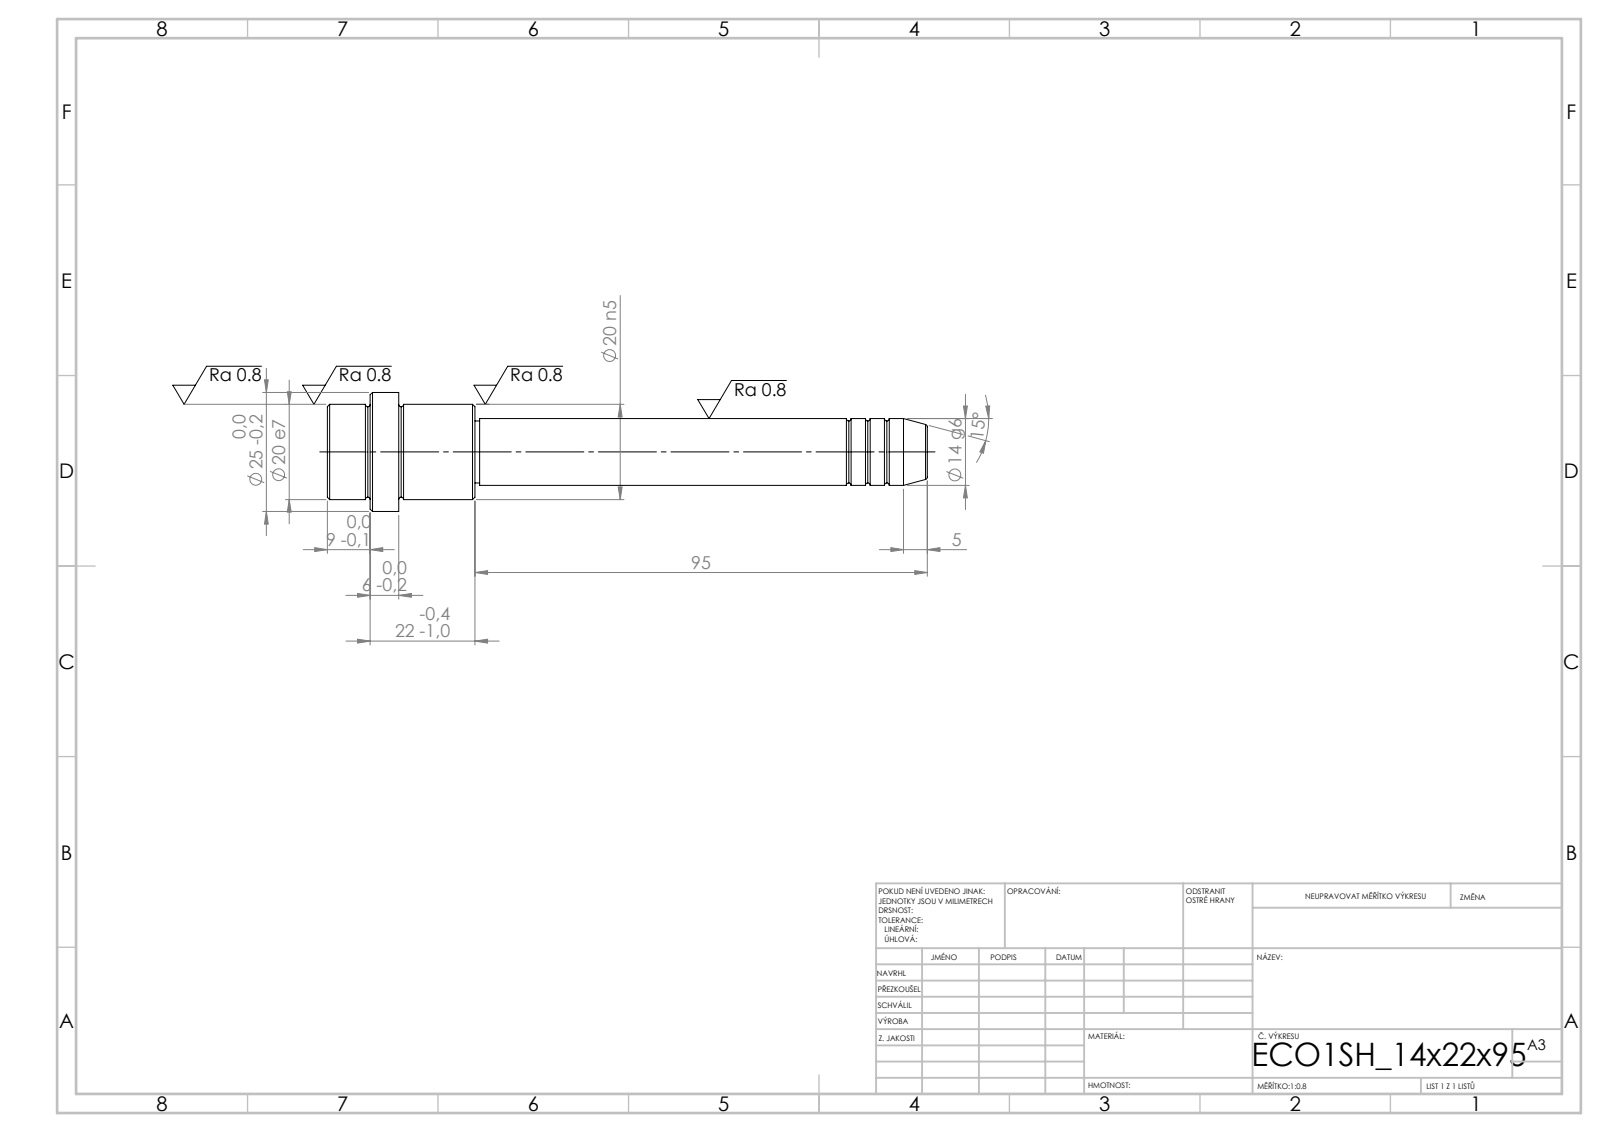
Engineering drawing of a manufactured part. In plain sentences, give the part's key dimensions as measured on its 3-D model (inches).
Its 3-D file was written by "SolidWorks 2019 (CONFIG_CONTROL_DESIGN)". It is 1 solid with 52 faces: 6 planar, 16 cylindrical and 30 other. Overall it measures 4.961 by 0.984 by 0.984 inches. Its volume is 1.534 cubic inches and its surface area 11.22 square inches. Round bosses or shafts: 1 of diameter 0.984, 1 of diameter 0.787, 1 of diameter 0.551, 1 of diameter 0.512. The main face-to-face distances are 0.591, 0.63, 1.22, 0.866, 0.236, 0.354, 3.74, 4.37, 4.606, 4.961.
